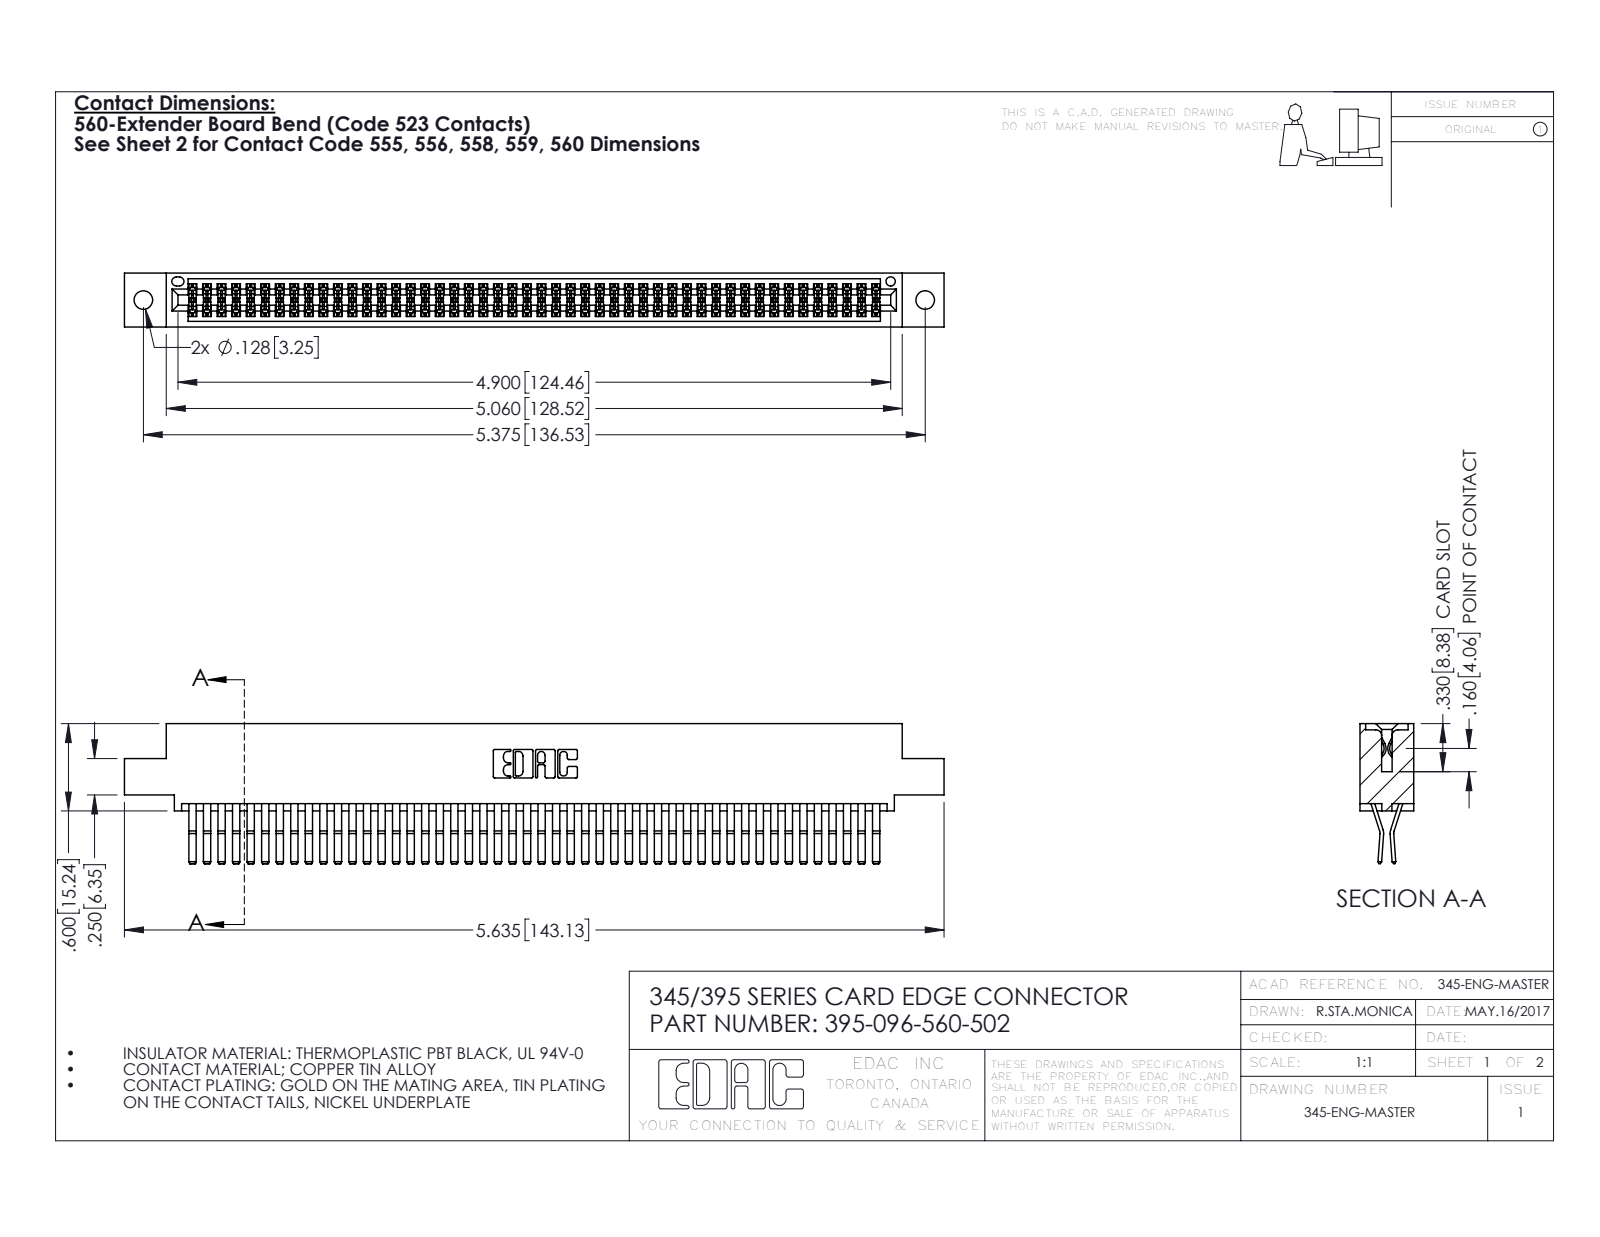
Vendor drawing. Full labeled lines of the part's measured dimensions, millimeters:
Part name (STEP PRODUCT): 345-292-001_560 Tail; 395-096-560-502; 345 Part_0.110 Offset - 0.128 Dia
STEP written by: SolidWorks 2016 (CONFIG_CONTROL_DESIGN)
Units: millimetres
Bodies: 97 solids, 5122 faces (3252 planar, 1870 cylindrical, 0 other)
Overall size (bounding box): 143.1 × 24.4 × 9.4
Volume: 14 500 mm³ · Surface area: 22 950 mm²
Round holes (diameter × count): ⌀3.3 ×2, ⌀1.6 ×1
Partial cylindrical surfaces — rounded edges, fillets, slot ends (radius × count): R0.2 ×144, R0.3 ×22, R0.2 ×6, R0.8 ×6, R0.7 ×3, R0.3 ×2, R0.4 ×2, R0.5 ×2
Main face-to-face distances: 0.6, 7.6, 1.8, 9.4, 5.1, 2.5, 6.9, 5.7, 4.4, 3.8
Hole centre spacings: 6.9, 130.5, 136.5
